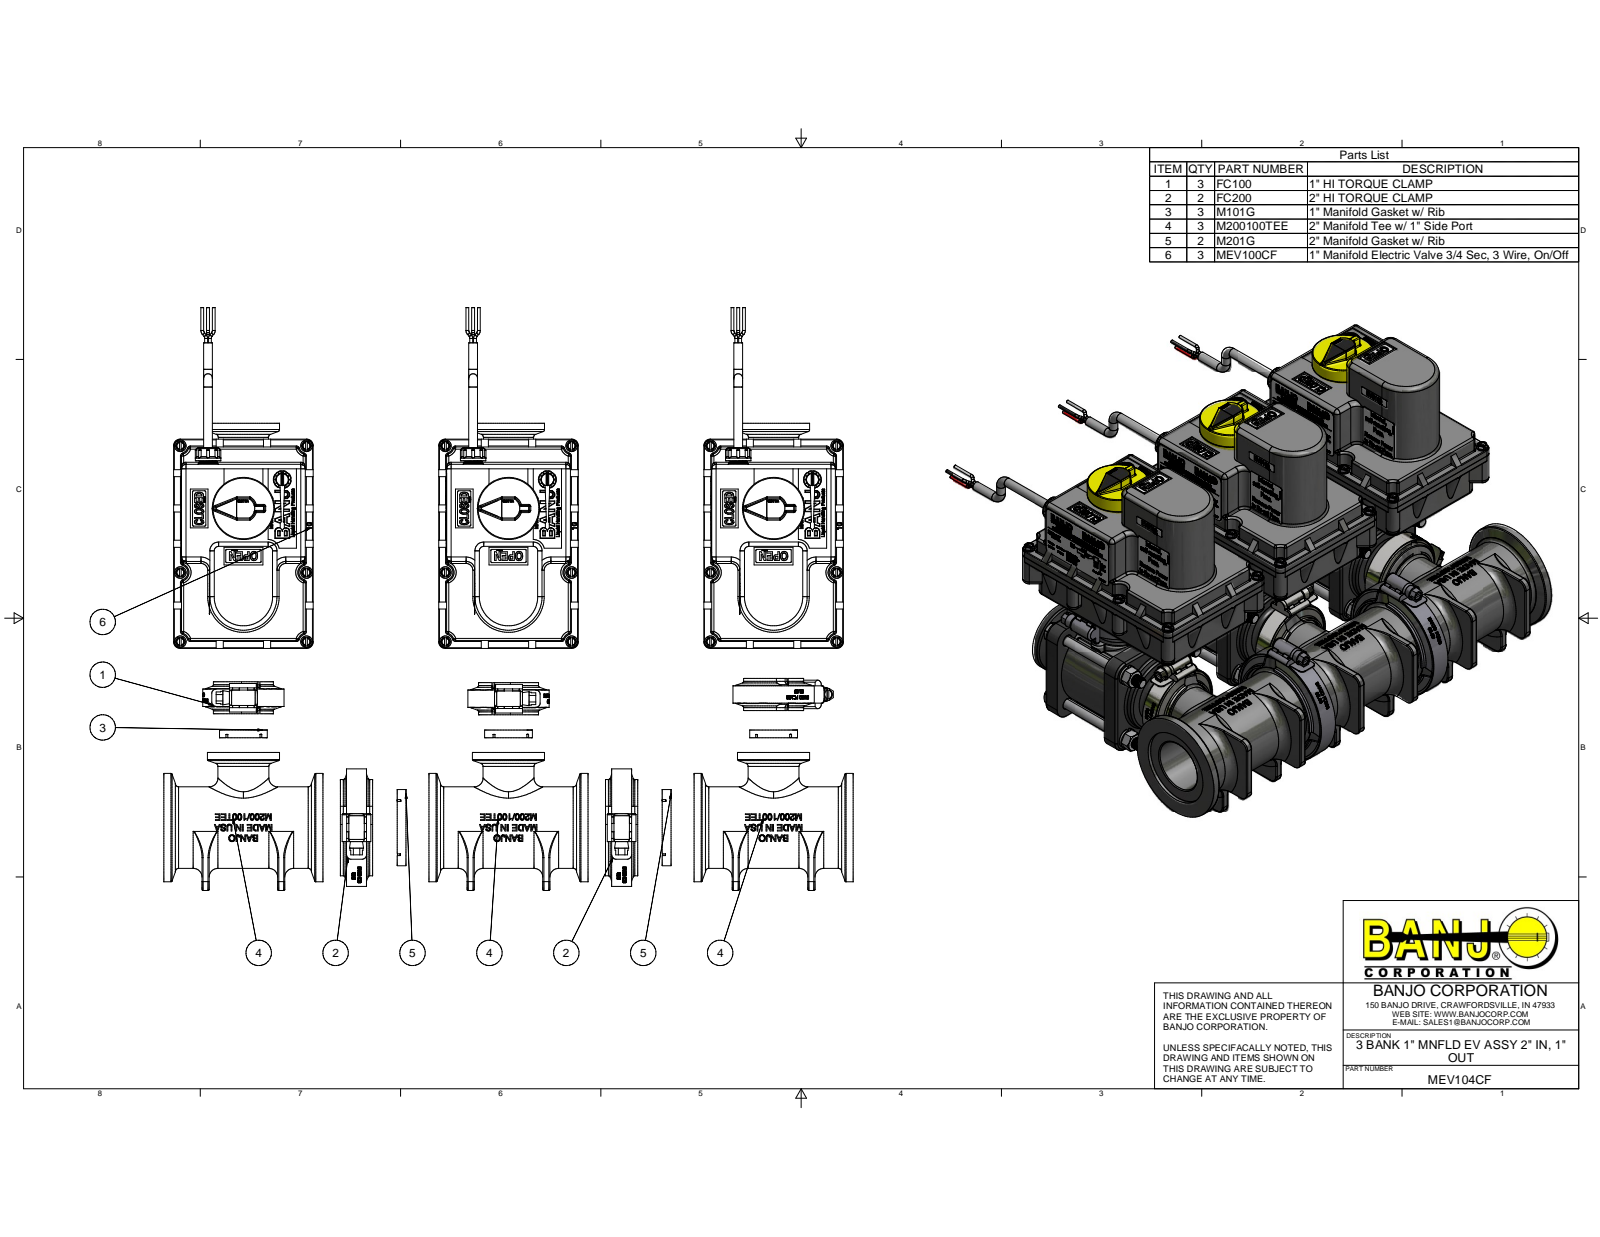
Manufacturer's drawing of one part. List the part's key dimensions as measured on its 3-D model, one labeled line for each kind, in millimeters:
Part name (STEP PRODUCT): MEV10254AX; MEV10254A; VE10155SSH; MEV10151SS (+8 more)
STEP written by: Autodesk Inventor 2014 (AUTOMOTIVE_DESIGN)
Units: millimetres
Bodies: 217 solids, 37343 faces (17383 planar, 5327 cylindrical, 14633 other)
Overall size (bounding box): 342.9 × 305.14 × 227.27
Volume: 3 497 000 mm³ · Surface area: 1 448 000 mm²
Round holes (diameter × count): ⌀1.52 ×24, ⌀2.79 ×18, ⌀3.05 ×18, ⌀3.81 ×18, ⌀4.06 ×18, ⌀4.47 ×18, ⌀5.08 ×18, ⌀4.44 ×12, ⌀6.41 ×12, ⌀8.18 ×12, ⌀8.89 ×12, ⌀4.32 ×9
Round bosses / shafts (diameter × count): ⌀6.82 ×180, ⌀2.03 ×27, ⌀6.35 ×21, ⌀8.33 ×18, ⌀3.51 ×18, ⌀1.9 ×15, ⌀14.81 ×12, ⌀8.03 ×12
Partial cylindrical surfaces — rounded edges, fillets, slot ends (radius × count): R0.76 ×769, R0.51 ×226, R1.52 ×152, R3.17 ×93, R1.59 ×53, R6.35 ×49, R9.53 ×48, R4.76 ×30
Main face-to-face distances: 114.3, 27.94, 5.08, 3.17, 33.02, 45.72, 3.18, 228.6, 21.71, 22.86
Hole centre spacings: 114.3, 39.3, 55.58, 42.68, 52.27, 90.86, 127.1, 144.78
